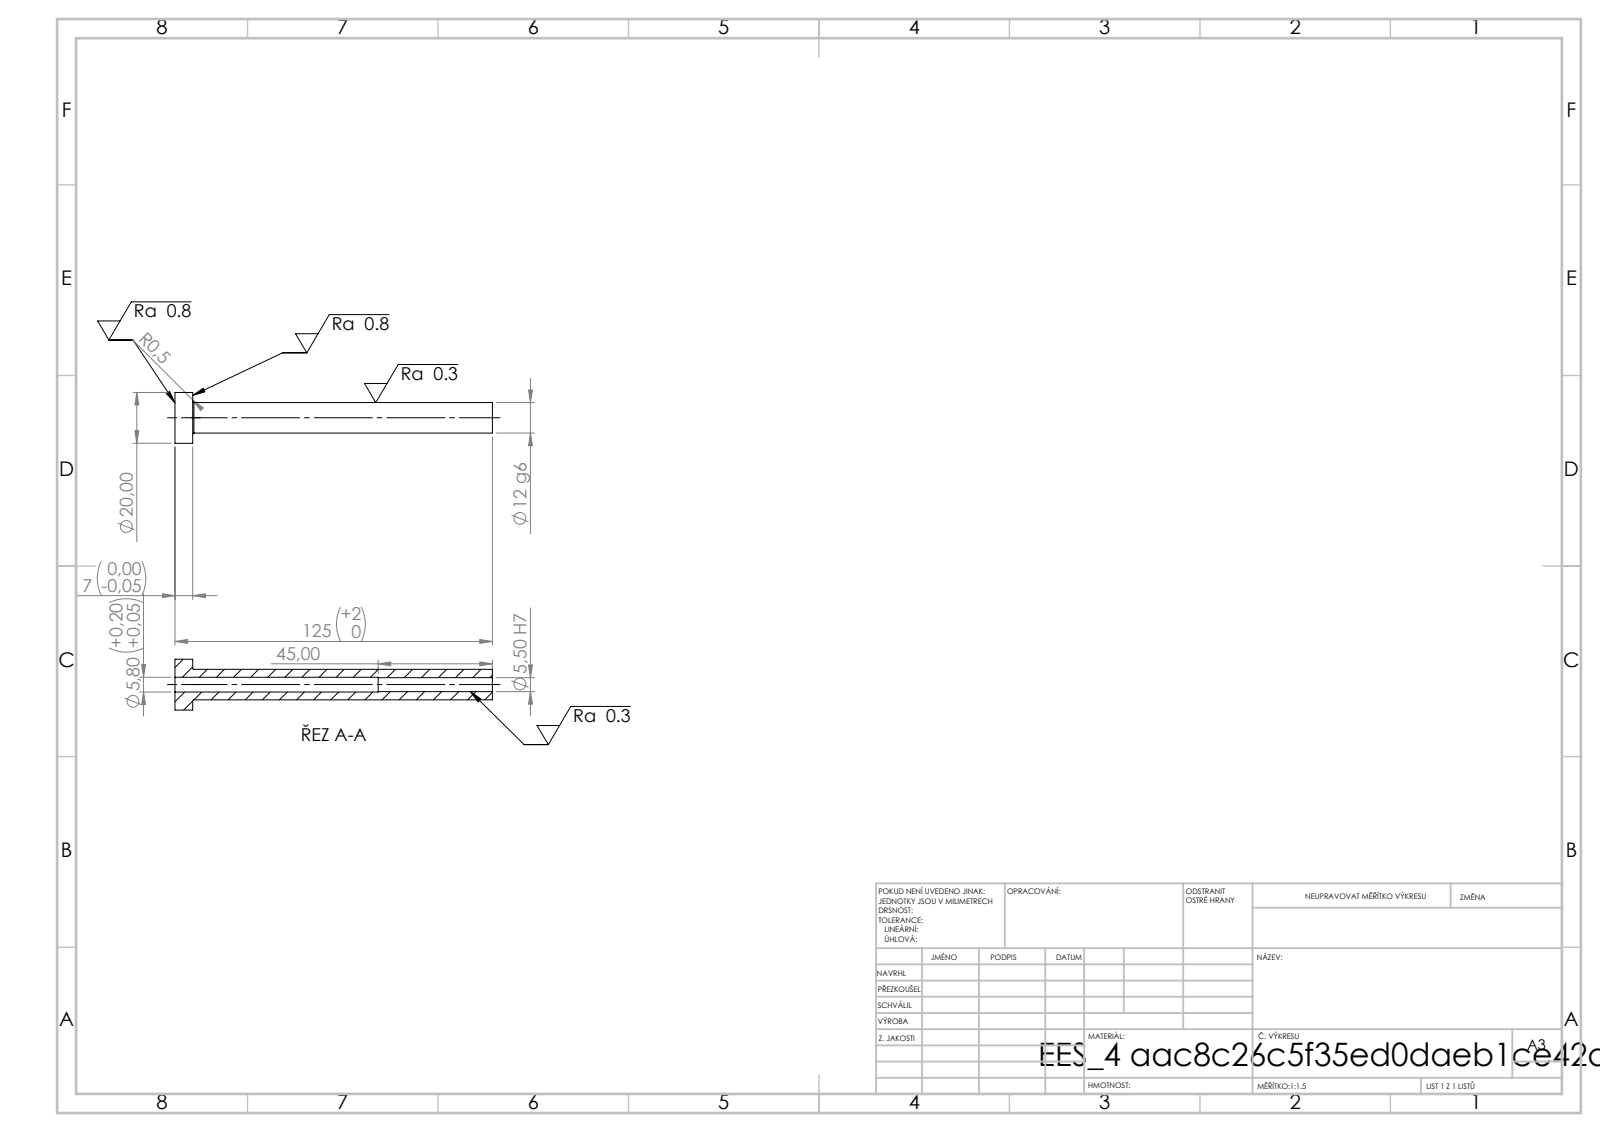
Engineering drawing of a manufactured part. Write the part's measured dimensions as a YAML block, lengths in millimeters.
step_written_by: "SolidWorks 2019 (CONFIG_CONTROL_DESIGN)"
units: millimeters
bodies: {solids: 1, faces: 14, planar: 4, cylindrical: 8, other: 2}
overall_size: [125, 20, 20]
volume: 12364
surface_area: 7696
round_holes:
  - {diameter: 5.5, count: 1}
  - {diameter: 5.8, count: 1}
round_bosses_or_shafts:
  - {diameter: 20, count: 1}
  - {diameter: 12, count: 1}
face_to_face_distances: [7, 125, 118, 80, 73, 45]
